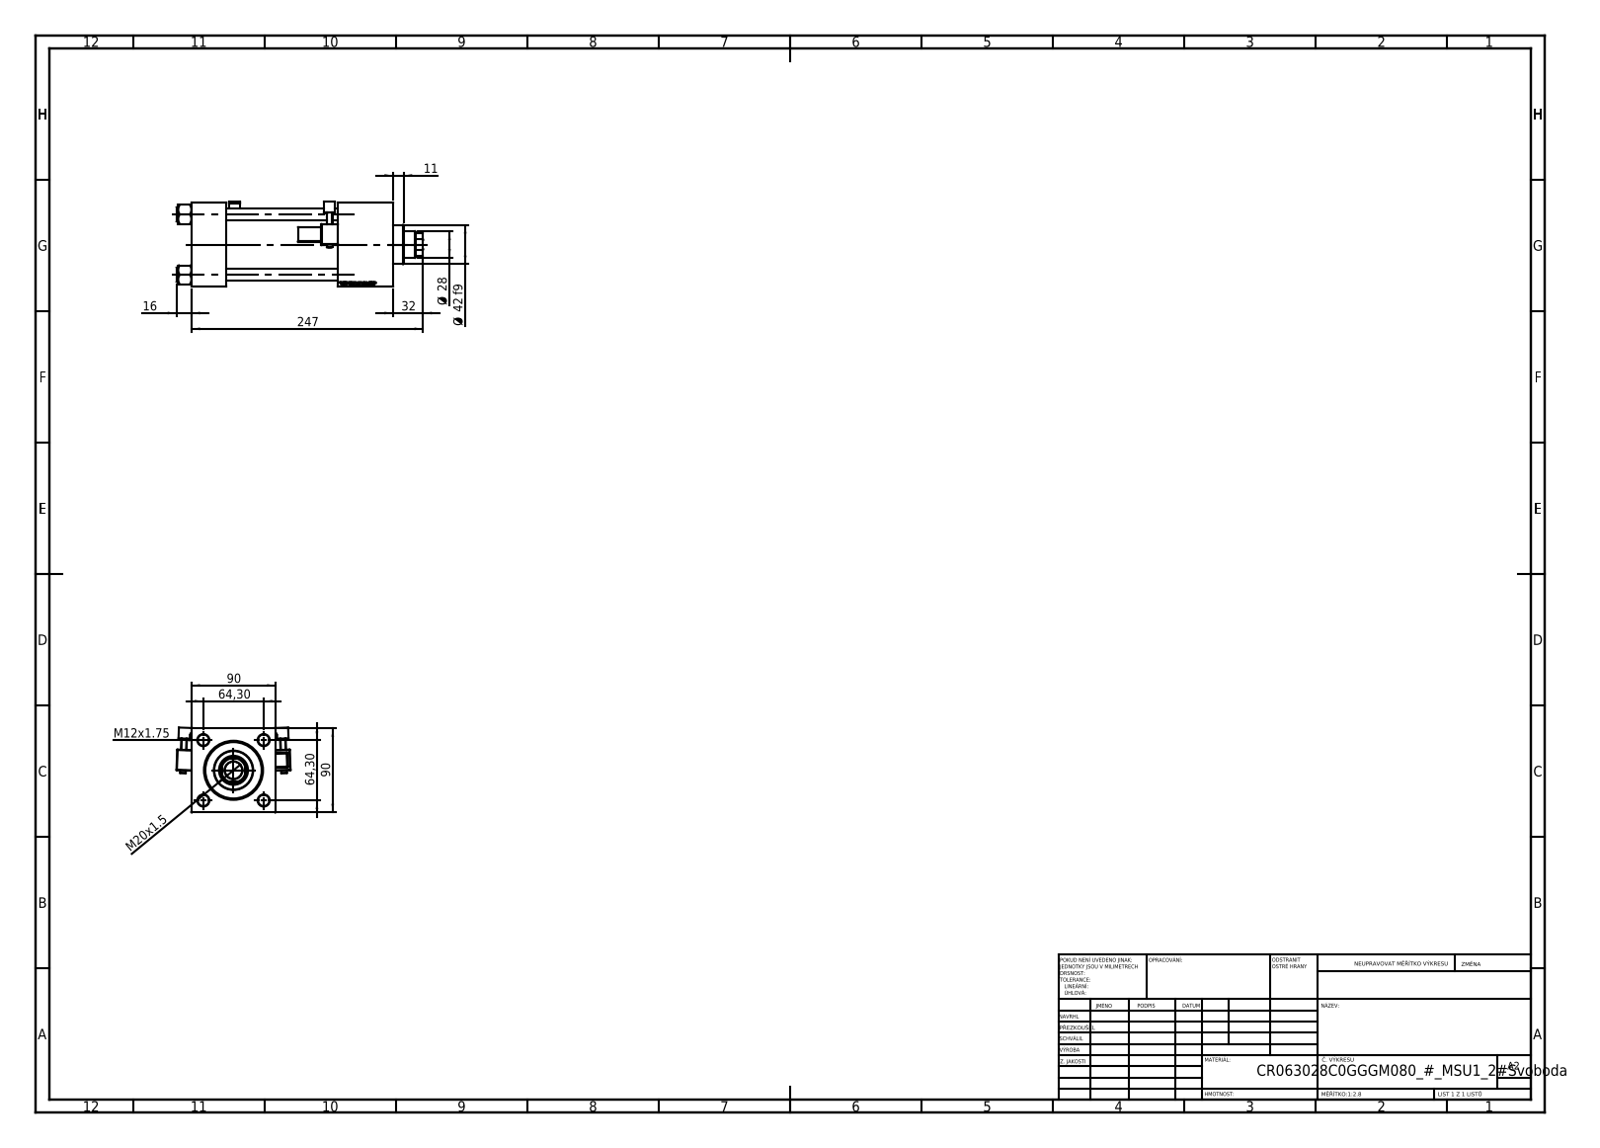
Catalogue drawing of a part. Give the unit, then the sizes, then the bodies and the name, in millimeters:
Units: millimetres
Overall size (bounding box): 263 × 121.57 × 90.53
Round holes (diameter × count): ⌀12 ×4, ⌀7 ×2, ⌀20.96 ×2, ⌀30 ×2, ⌀18.5 ×1, ⌀28 ×1, ⌀31 ×1, ⌀50 ×1, ⌀60 ×1, ⌀63 ×1
Round bosses / shafts (diameter × count): ⌀15 ×4, ⌀6 ×2, ⌀69 ×1, ⌀42 ×1
Partial cylindrical surfaces — rounded edges, fillets, slot ends (radius × count): R0.5 ×48, R1 ×2, R2.5 ×2, R4 ×2, R13.5 ×1
Main face-to-face distances: 90, 37, 215, 178, 59, 156, 119, 186.3, 149.3, 30.3
Hole centre spacings: 45.47, 64.3, 90.93, 157.5
Volume: 1 089 000 mm³ · Surface area: 230 610 mm²
Bodies: 13 solids, 1303 faces (584 planar, 147 cylindrical, 572 other)
Part name (STEP PRODUCT): V215CR_C_TYCINKA; NUT_M5_C; V215CR_VCP_C; V215_VC_A (+2 more)
STEP written by: SolidWorks 2019 (CONFIG_CONTROL_DESIGN)
